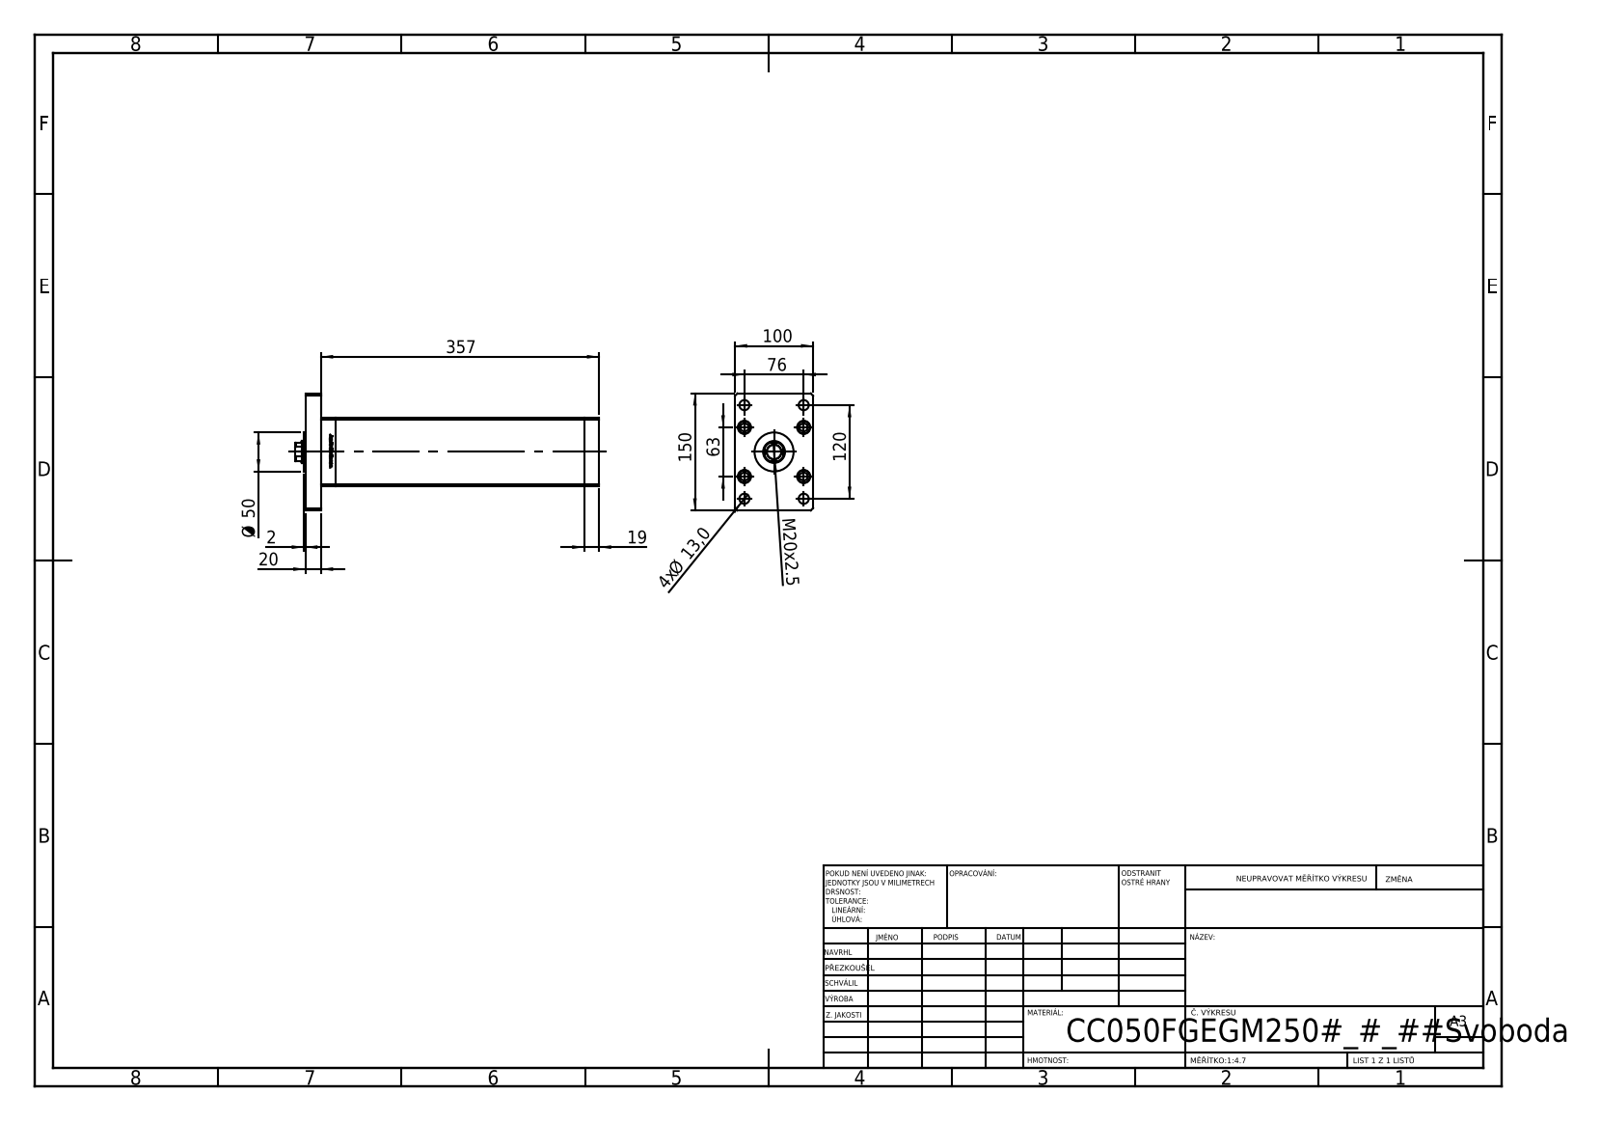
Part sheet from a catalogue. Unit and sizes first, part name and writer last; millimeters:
Units: millimetres
Overall size (bounding box): 389.5 × 150 × 100
Round holes (diameter × count): ⌀13.5 ×7, ⌀18 ×7, ⌀12 ×4, ⌀13 ×4, ⌀17 ×4, ⌀2 ×2, ⌀13.16 ×2, ⌀18.5 ×1, ⌀28 ×1, ⌀29.5 ×1
Round bosses / shafts (diameter × count): ⌀8 ×9, ⌀17 ×5, ⌀50 ×1
Partial cylindrical surfaces — rounded edges, fillets, slot ends (radius × count): R0.93 ×2, R13.5 ×1
Main face-to-face distances: 100, 87, 19, 337.5, 20, 318.5, 39, 357.5, 356.5, 376.5
Hole centre spacings: 34, 18.59, 28.5, 37.13, 39.64, 49.36, 57.95, 71.02
Volume: 2 920 000 mm³ · Surface area: 367 952 mm²
Bodies: 19 solids, 1311 faces (517 planar, 188 cylindrical, 606 other)
Part name (STEP PRODUCT): V220C BACK_F; V220C_F; V220C_F_MIDDLE; V220C_VC_F (+2 more)
STEP written by: SolidWorks 2019 (CONFIG_CONTROL_DESIGN)
